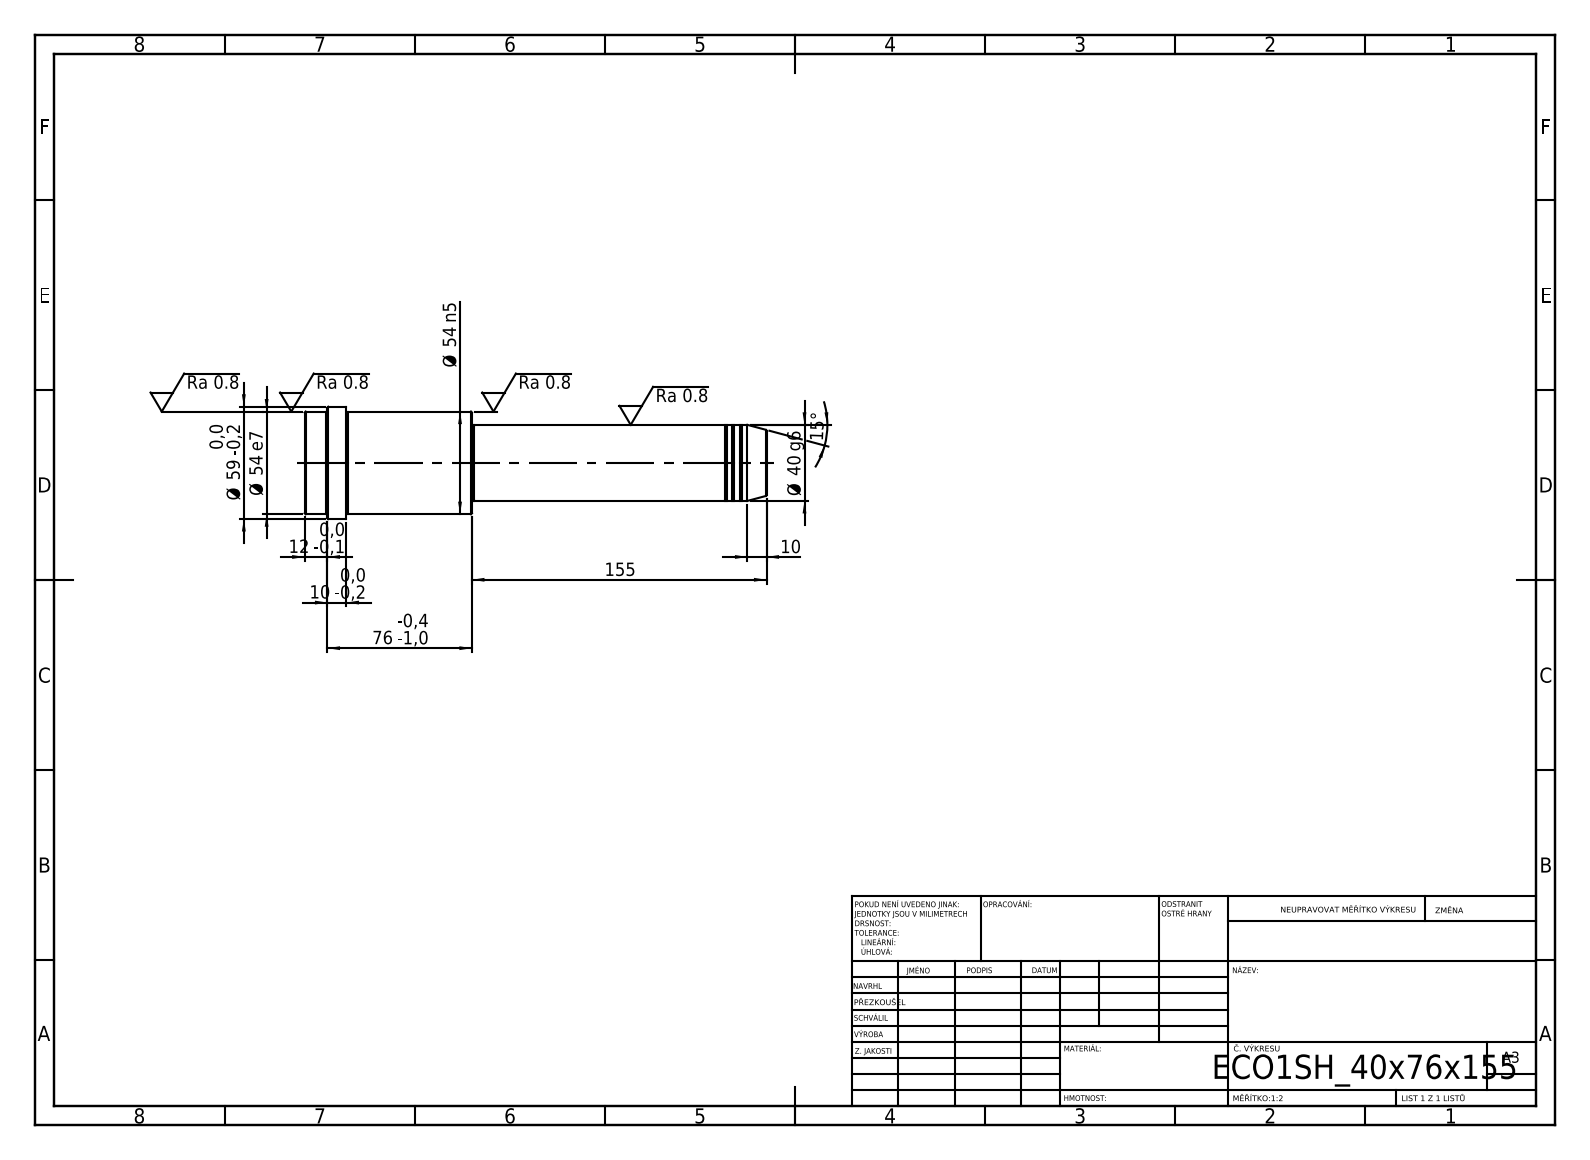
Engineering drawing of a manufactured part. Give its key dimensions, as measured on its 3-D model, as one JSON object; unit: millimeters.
{"step_written_by": "SolidWorks 2019 (CONFIG_CONTROL_DESIGN)", "units": "millimeters", "bodies": {"solids": 1, "faces": 52, "planar": 6, "cylindrical": 16, "other": 30}, "overall_size": [243, 59, 59], "volume_mm3": 398738, "surface_area_mm2": 40022, "round_bosses_or_shafts": [[59, 1], [54, 1], [40, 1], [39, 1]], "face_to_face_distances": [88, 155, 243, 221, 66, 22, 231, 76, 10, 12]}
